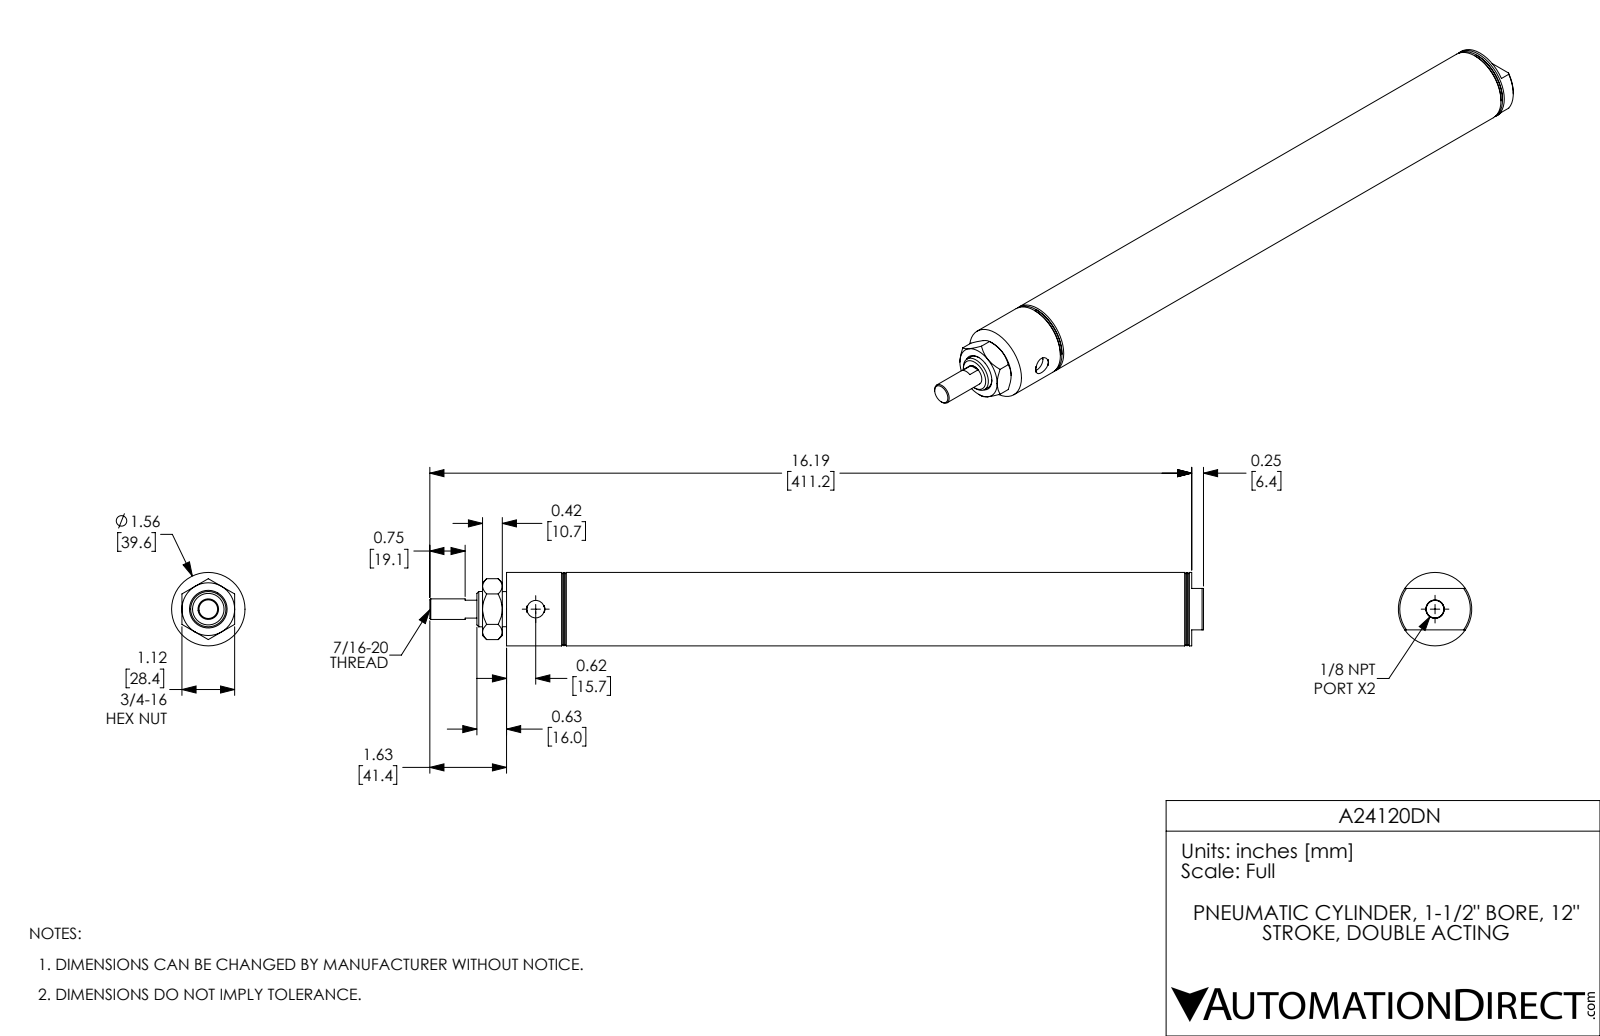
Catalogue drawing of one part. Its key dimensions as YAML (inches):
part_name: "A24120DN; A24120DN_Mounting Nut_D-3556; A24120DN-Rod; A24120DN-MainBody"
step_written_by: "SolidWorks 2017 (AUTOMOTIVE_DESIGN)"
units: inches
bodies: {solids: 3, faces: 104, planar: 32, cylindrical: 24, other: 48}
overall_size: [16.44, 1.56, 1.56]
volume: 9.378
surface_area: 173.5
round_holes:
  - {diameter: 0.374, count: 2}
  - {diameter: 0.437, count: 1}
  - {diameter: 0.75, count: 1}
  - {diameter: 1.5, count: 1}
round_bosses_or_shafts:
  - {diameter: 1.56, count: 1}
  - {diameter: 0.746, count: 1}
face_to_face_distances: [12.5, 0.5, 12, 13.84, 13.34, 1.34, 0.97, 1.47, 13.47, 14.81]
